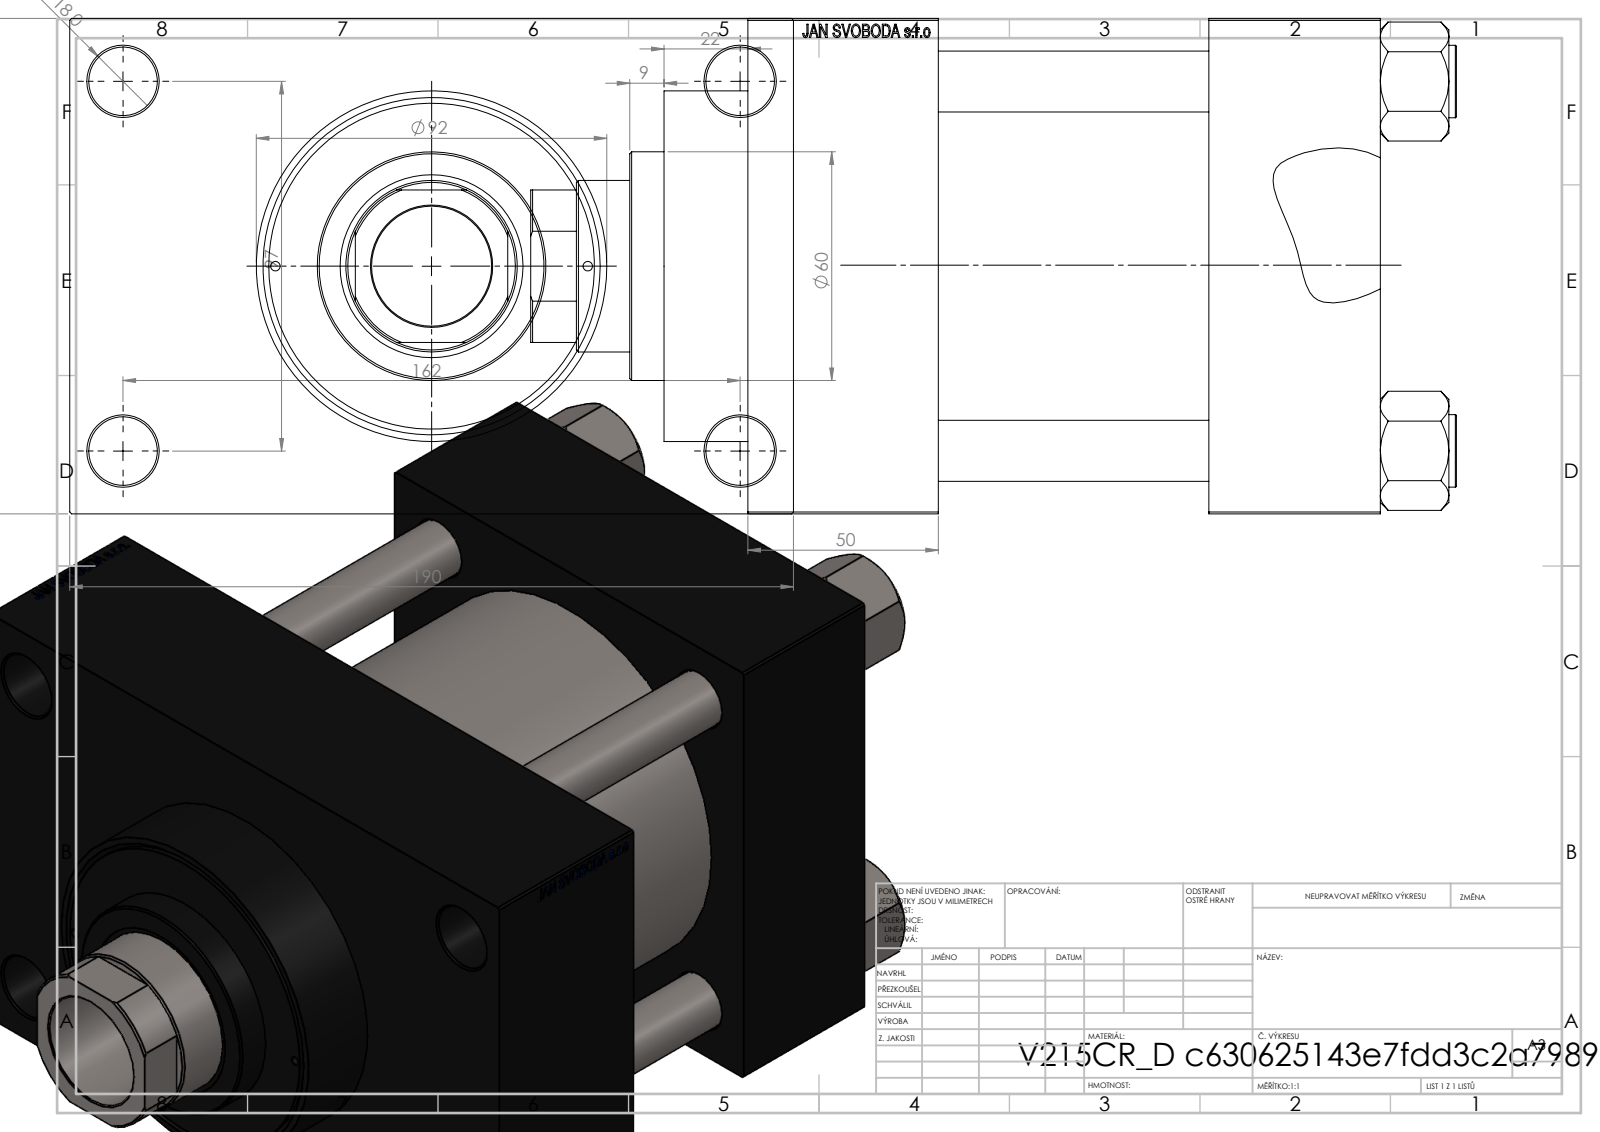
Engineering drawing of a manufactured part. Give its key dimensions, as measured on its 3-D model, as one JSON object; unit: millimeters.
{"part_name": "NUT_M5_D; V215_VC_A; V215CR_D_Body; V215CR_D_TYCINKA (+1 more)", "step_written_by": "SolidWorks 2019 (CONFIG_CONTROL_DESIGN)", "units": "millimeters", "bodies": {"solids": 11, "faces": 1159, "planar": 547, "cylindrical": 92, "other": 520}, "overall_size": [243, 190, 130], "volume_mm3": 2590000, "surface_area_mm2": 354722, "round_holes": [[16, 4], [18, 4], [2.5, 2], [7, 2], [26.44, 2], [35, 2], [31.5, 1], [45, 1], [48, 1], [76, 1], [85.5, 1], [100, 1]], "round_bosses_or_shafts": [[19, 4], [106, 1], [92, 1], [60, 1]], "partial_cylinders_radius": [[22, 1]], "face_to_face_distances": [130, 45, 116, 71, 166, 121, 50, 30, 160, 20], "hole_center_spacings": [32.55, 49.02, 62.87, 68.52, 94.41, 96.9, 101.73, 102.27]}
